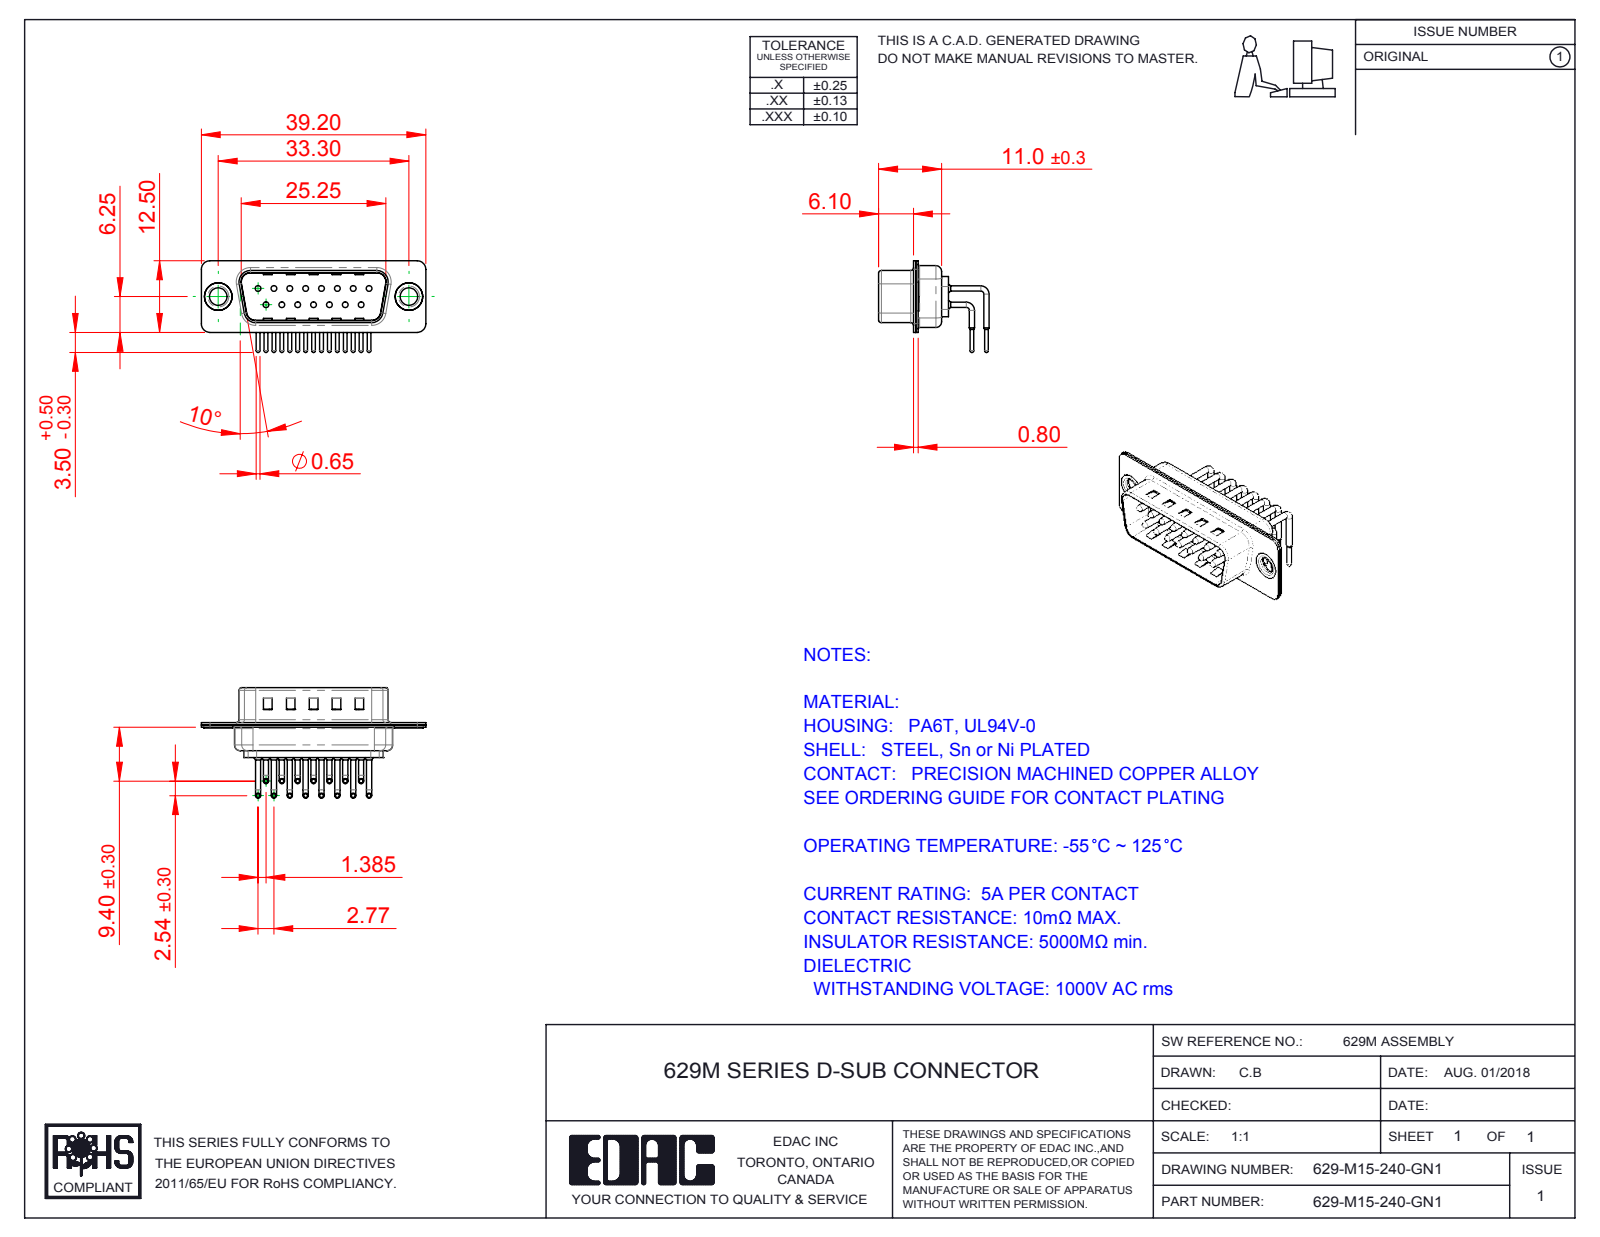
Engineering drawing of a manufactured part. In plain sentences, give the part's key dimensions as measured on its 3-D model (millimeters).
The part is named "629M Shell Front_15 Contacts; 629M Housing_15 Contacts; 629M Shell Rear_15 Contacts; 629M Contact Row 1 (+3 more)". Its 3-D file was written by "SolidWorks 2016 (CONFIG_CONTROL_DESIGN)". It is 20 solids with 1964 faces: 1099 planar, 657 cylindrical and 208 other. Overall it measures 39.2 by 19.29 by 16 millimeters. Its volume is 1 881 cubic millimeters and its surface area 5 213 square millimeters. Round holes: 15 of diameter 1, 15 of diameter 1.7, 15 of diameter 2, 2 of diameter 3.05, 2 of diameter 4, 2 of diameter 4.8. Round bosses or shafts: 30 of diameter 0.9, 15 of diameter 1.5, 15 of diameter 0.65, 2 of diameter 5, 2 of diameter 4.9, 2 of diameter 3.55. Partial cylindrical surfaces (rounded edges, fillets, slot ends): 16 of radius 1.5, 15 of radius 1.01, 12 of radius 2, 8 of radius 0.5, 8 of radius 1.6, 4 of radius 0.25, 4 of radius 0.6, 4 of radius 0.65. The main face-to-face distances are 0.4, 0.85, 9.55, 8.7, 1.25, 0.8, 10.4, 1.5, 0.35, 1.9. The hole center spacings are 3.16, 2.77, 5.54, 8.31, 11.08, 5.03, 5.04, 7.48.
